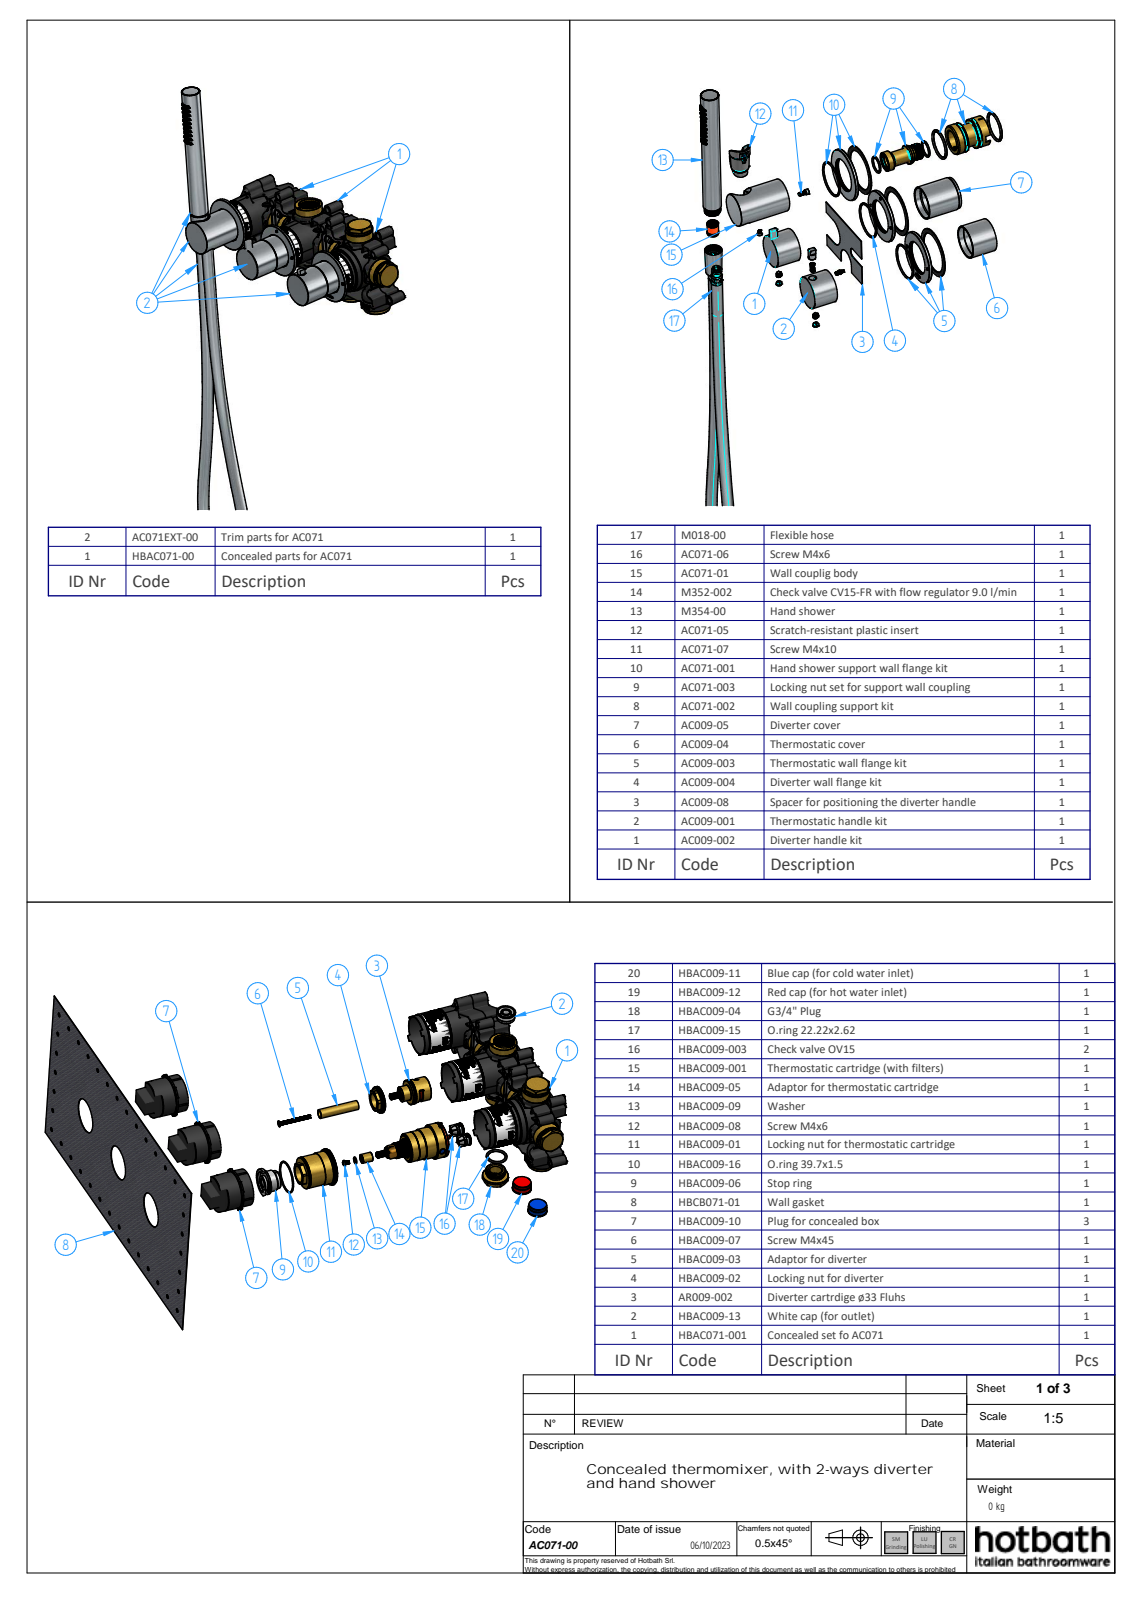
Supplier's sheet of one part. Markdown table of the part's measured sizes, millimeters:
| quantity | value |
| --- | --- |
| part name | AC071EXT-00; M354-00_oa_0; C101014_02100ZZ; A133037_13400ZZ (+8 more) |
| STEP written by | Solid Edge (AUTOMOTIVE_DESIGN) |
| units | millimeters |
| bodies | 19 solids, 2353 faces (588 planar, 624 cylindrical, 1141 other) |
| overall size | 762.42 × 322.45 × 100.49 |
| volume | 300 458 mm³ |
| surface area | 238 761 mm² |
| round holes (diameter × count) | 3.2 × 41, 8 × 4, 10 × 3, 44.5 × 3, 47.7 × 3, 5 × 2, 6.4 × 2, 12.1 × 2, 41.2 × 2, 3.3 × 1, 4.1 × 1, 4.5 × 1 |
| round bosses / shafts (diameter × count) | 44 × 3, 14.7 × 2, 7.6 × 2, 42.5 × 1, 24 × 1, 21.8 × 1, 21.6 × 1, 21.17 × 1 |
| partial cylindrical surfaces (radius × count) | 0.5 × 85, 0.3 × 56, 0.1 × 18, 0.2 × 10, 1 × 8, 2 × 7, 0.15 × 4, 0.35 × 4 |
| main face-to-face distances | 3.5, 52.1, 55.6, 0.5, 4, 56.1, 0.9, 52, 55.5, 56 |
| hole center spacings | 7.21, 12.65, 12, 6, 18.44, 4, 24.33, 10 |
